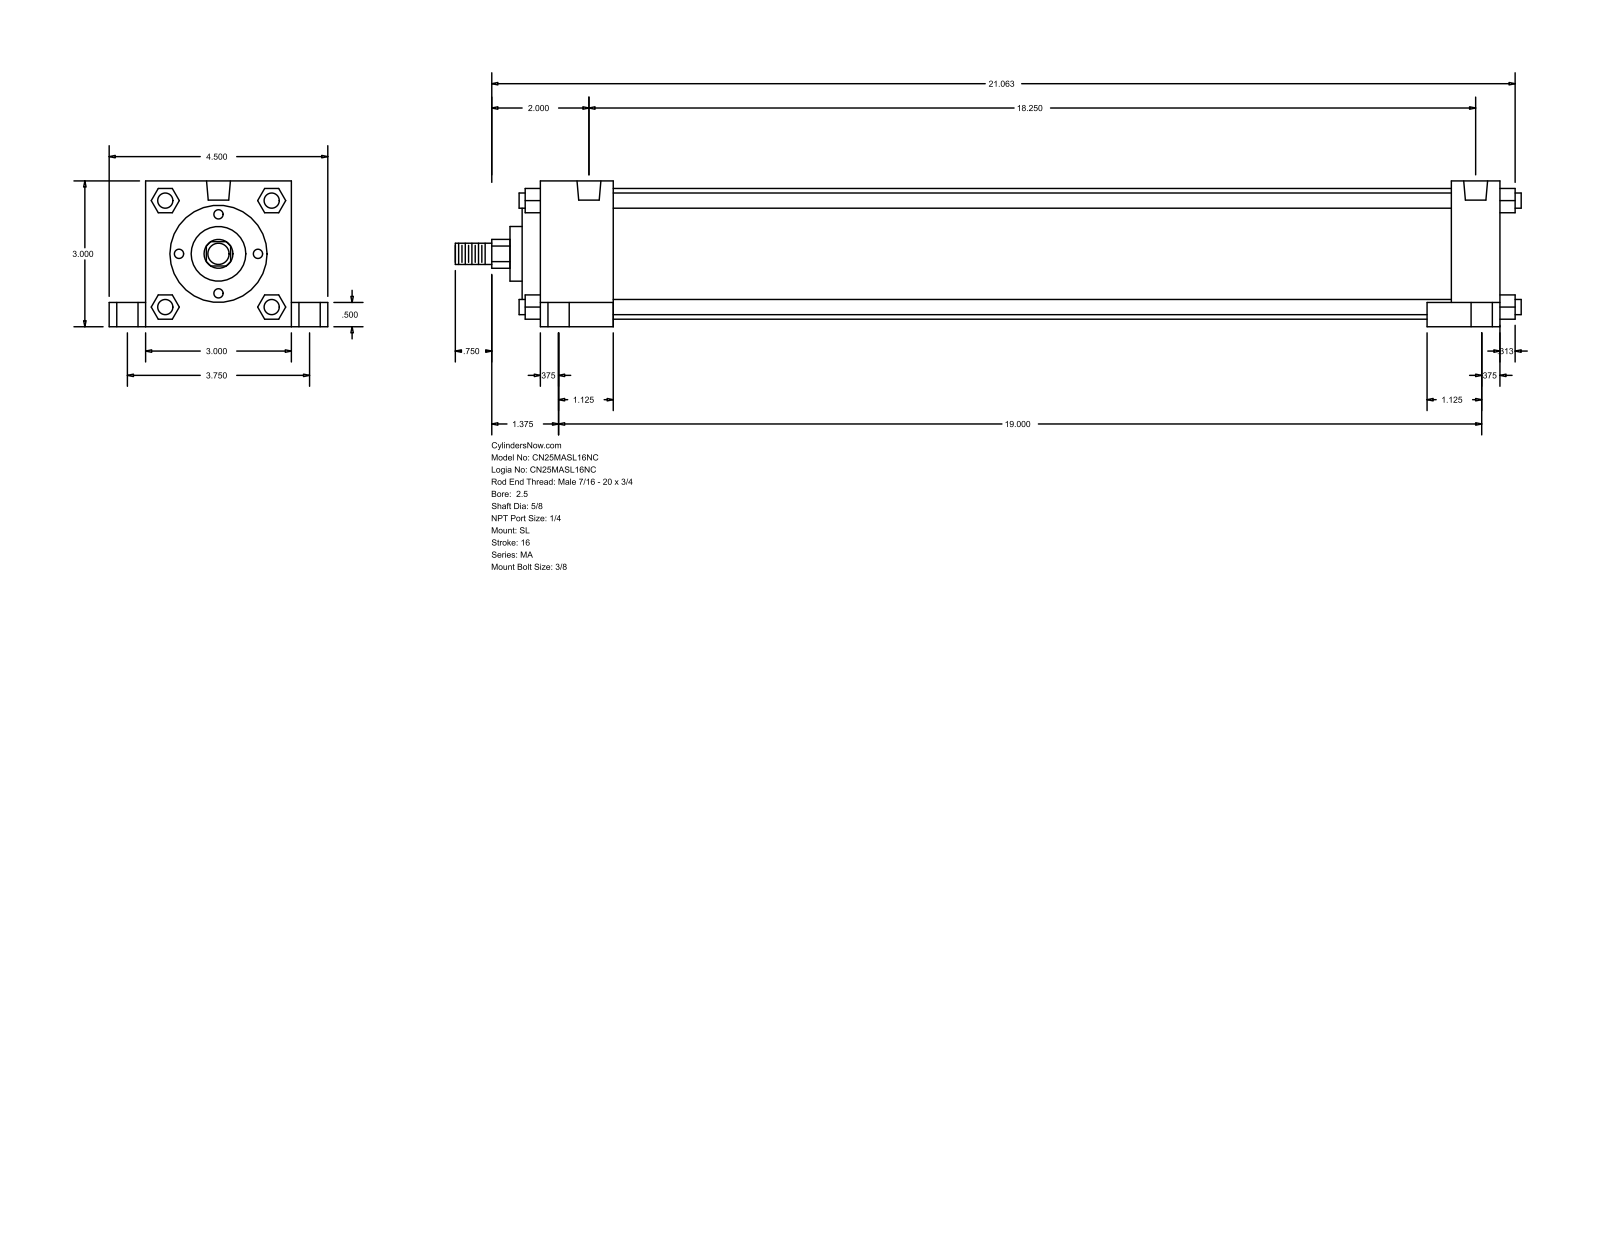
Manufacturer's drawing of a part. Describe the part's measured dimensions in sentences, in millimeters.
The part is named "MA_SL__0250_0.625". Its 3-D file was written by "GSSL Pune (CONFIG_CONTROL_DESIGN)". It is 0 solids with 150 faces: 113 planar, 37 cylindrical and 0 other. Overall it measures 557.21 by 114.3 by 76.2 millimeters. Round holes: 4 of diameter 7.94, 4 of diameter 11.11, 4 of diameter 17.46, 2 of diameter 12.49. Round bosses or shafts: 4 of diameter 7.94, 1 of diameter 68.33, 1 of diameter 50.8, 1 of diameter 28.57, 1 of diameter 15.88, 1 of diameter 11.11. Partial cylindrical surfaces (rounded edges, fillets, slot ends): 1 of radius 7.54. The main face-to-face distances are 76.2, 501.65, 12.7, 438.15, 25.4, 38.1, 463.55, 476.25, 19.05, 63.5. The hole center spacings are 47.73, 50.2, 95.24, 463.55, 469.14, 481.79, 482.6, 491.91.
